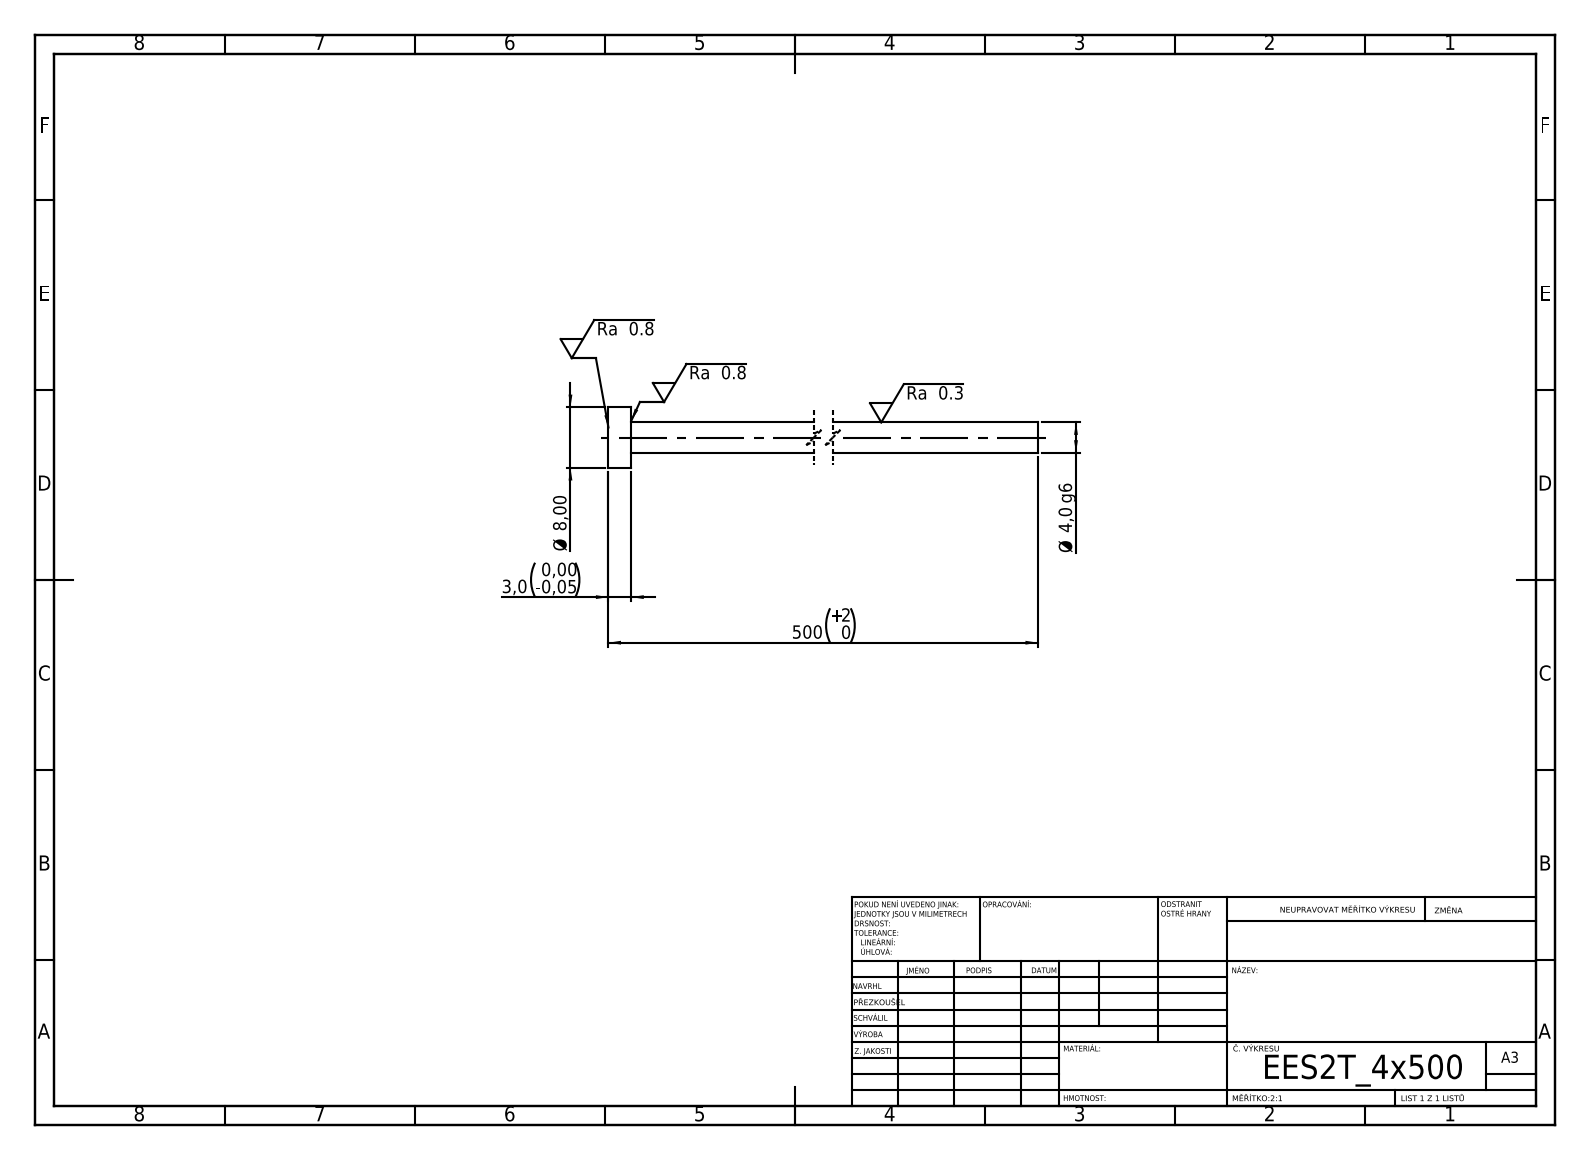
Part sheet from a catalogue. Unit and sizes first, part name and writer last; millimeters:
Units: millimetres
Overall size (bounding box): 500 × 8 × 8
Round bosses / shafts (diameter × count): ⌀8 ×1, ⌀4 ×1
Main face-to-face distances: 3, 500, 497
Volume: 6 396 mm³ · Surface area: 6 421 mm²
Bodies: 1 solid, 7 faces (3 planar, 4 cylindrical, 0 other)
STEP written by: SolidWorks 2019 (CONFIG_CONTROL_DESIGN)
